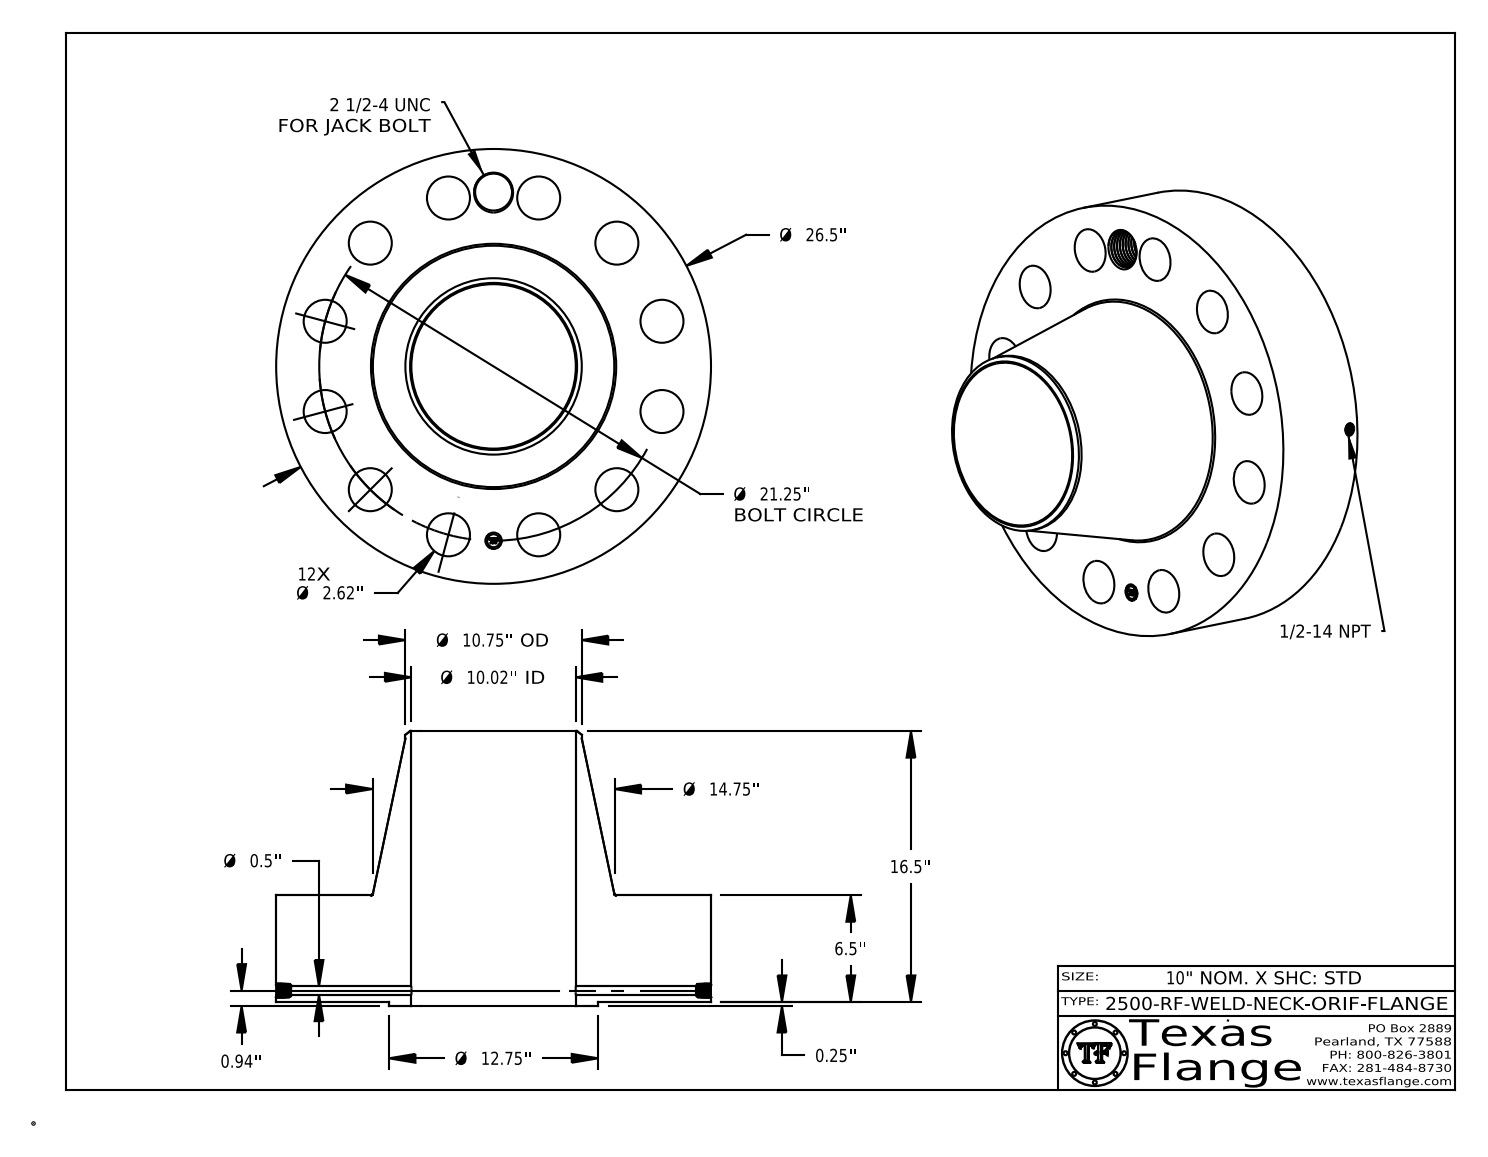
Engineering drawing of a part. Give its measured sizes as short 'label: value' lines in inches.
name: 2500-RF-WELD-NECK
written by: CATIA V5 STEP AP214 (AUTOMOTIVE_DESIGN)
unit: in
bodies: 1 solid, 843 faces (369 planar, 124 cylindrical, 350 other)
size: 26.5 × 26.5 × 16.75
volume: 3 112 in³; area: 2 945 in²
holes: 12× ⌀2.62, 1× ⌀0.5, 1× ⌀0.672, 1× ⌀1, 1× ⌀2.25, 1× ⌀10.02
bosses: 8× ⌀0.061, 1× ⌀26.5, 1× ⌀12.75, 1× ⌀10.75, 1× ⌀0.788
face distances: 6.5, 0.25, 6.75, 16.75, 16.5, 10, 0.015, 6.735, 6.485, 10.015
hole spacings: 10.625, 5.5, 15.026, 18.403, 20.526, 10.625, 21.25, 2.774
